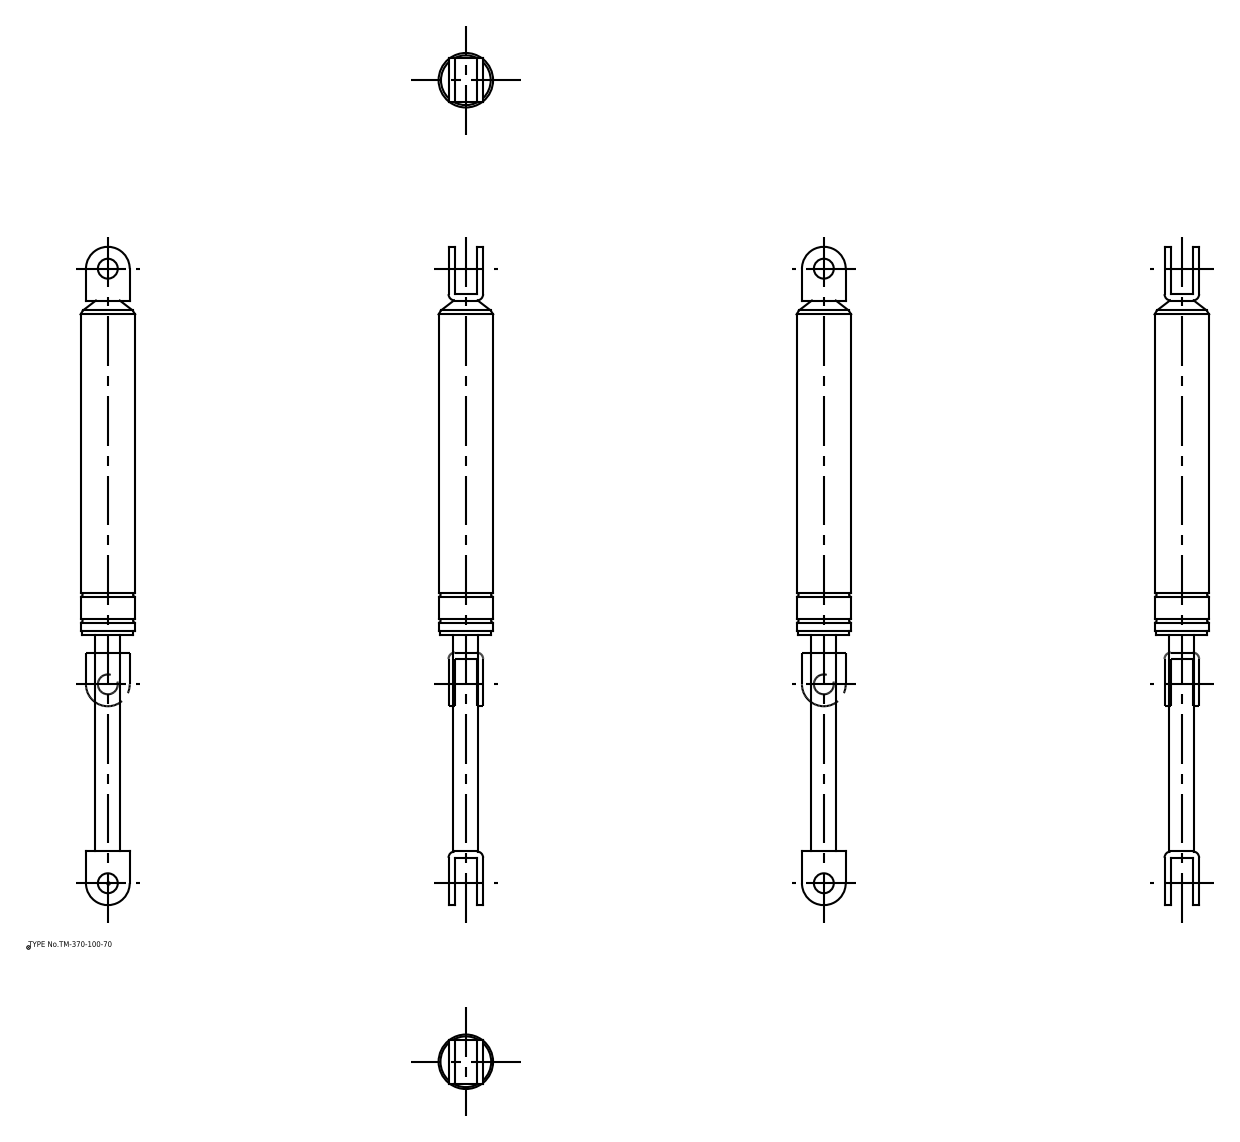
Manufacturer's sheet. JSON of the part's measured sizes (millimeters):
{"part_name": "TM_370_100_70; TM_370_100_70_div", "step_written_by": "spGate 16.7.1 (AUTOMOTIVE_DESIGN)", "units": "millimeters", "bodies": {"solids": 2, "faces": 64, "planar": 22, "cylindrical": 32, "other": 10}, "overall_size": [331, 28.2, 28.2], "volume_mm3": 118124, "surface_area_mm2": 25523, "round_holes": [[10, 2]], "round_bosses_or_shafts": [[28.2, 1], [27.4, 1], [25.5, 1], [12.5, 1]], "partial_cylinders_radius": [[3.2, 4], [11, 2]], "face_to_face_distances": [3.2, 14.2, 17.4, 11, 22, 280.2, 112.2, 283.4, 171.2, 168], "hole_center_spacings": [309]}
